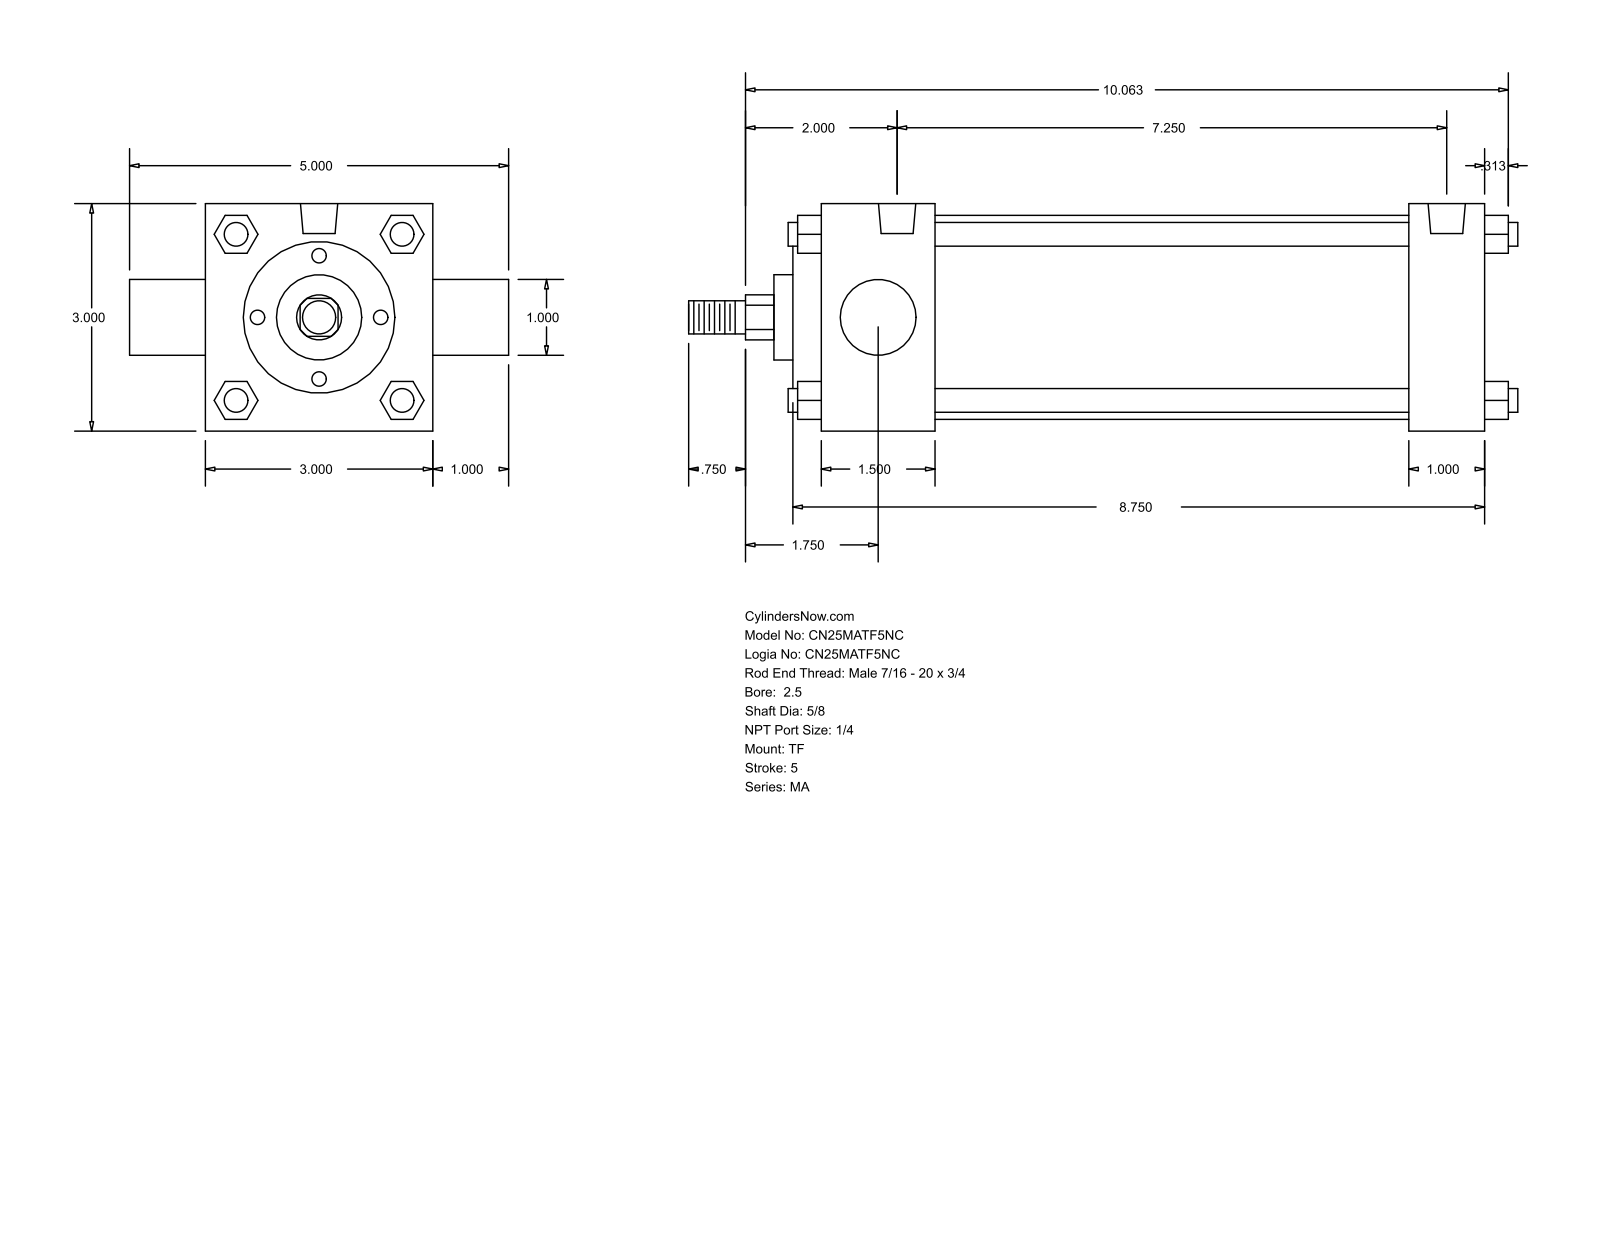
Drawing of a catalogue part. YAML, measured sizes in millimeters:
part_name: "MA_TF__0250_0.625"
step_written_by: "GSSL Pune (CONFIG_CONTROL_DESIGN)"
units: millimeters
bodies: {solids: 0, faces: 122, planar: 93, cylindrical: 29, other: 0}
overall_size: [277.81, 127, 76.2]
round_holes:
  - {diameter: 7.94, count: 3}
  - {diameter: 12.49, count: 2}
round_bosses_or_shafts:
  - {diameter: 7.94, count: 4}
  - {diameter: 68.33, count: 1}
  - {diameter: 50.8, count: 1}
  - {diameter: 28.57, count: 1}
  - {diameter: 25.4, count: 1}
  - {diameter: 15.88, count: 1}
  - {diameter: 11.11, count: 1}
partial_cylinders:
  - {radius: 7.54, count: 1}
face_to_face_distances: [76.2, 222.25, 25.4, 38.1, 196.85, 158.75, 184.15, 12.7, 9.52, 47.62]
hole_center_spacings: [184.15]
